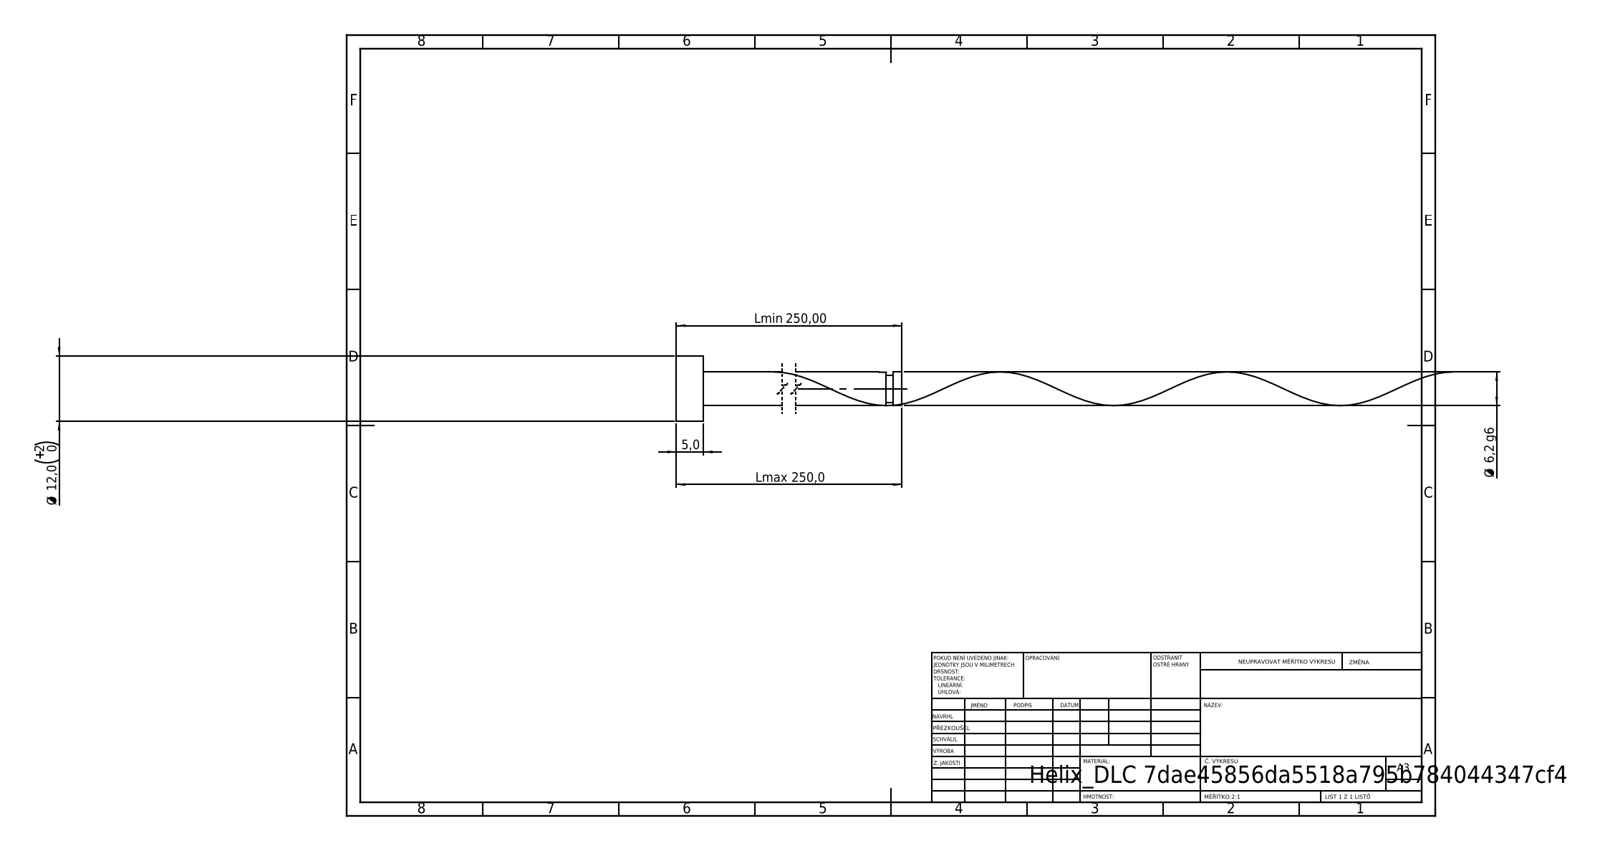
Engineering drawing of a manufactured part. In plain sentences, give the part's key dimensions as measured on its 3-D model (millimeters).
Its 3-D file was written by "SolidWorks 2019 (CONFIG_CONTROL_DESIGN)". It is 1 solid with 21 faces: 6 planar, 14 cylindrical and 1 other. Overall it measures 250 by 12 by 12 millimeters. Its volume is 7 876 cubic millimeters and its surface area 5 288 square millimeters. Round bosses or shafts: 1 of diameter 12, 1 of diameter 6.2, 1 of diameter 4.96. The main face-to-face distances are 5, 250, 245, 248.34, 243.34, 1.66, 247.1, 242.1, 1.24, 2.9.
